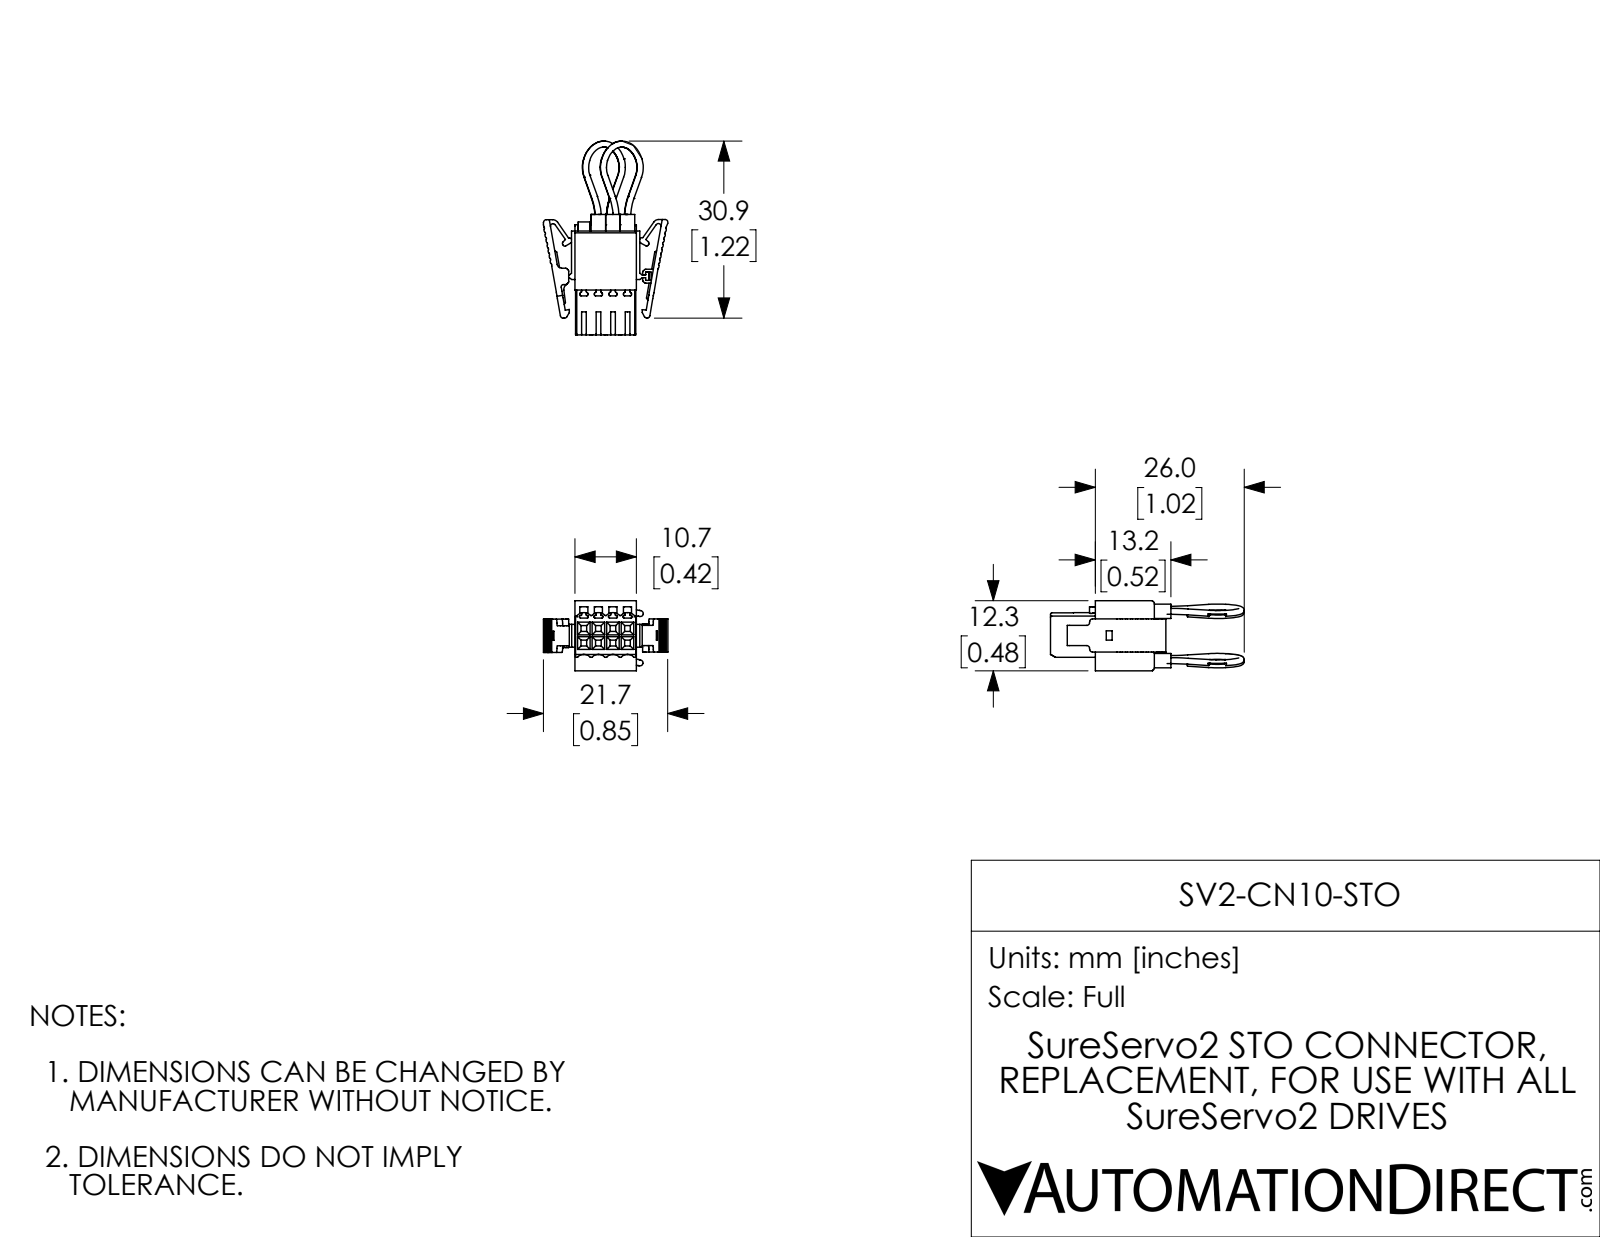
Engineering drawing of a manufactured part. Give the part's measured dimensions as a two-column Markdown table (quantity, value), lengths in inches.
| quantity | value |
| --- | --- |
| part name | SV2-CN10-STO |
| STEP written by | SolidWorks 2017 (AUTOMOTIVE_DESIGN) |
| units | inches |
| bodies | 1 solid, 703 faces (392 planar, 228 cylindrical, 83 other) |
| overall size | 1.331 × 0.855 × 0.482 |
| volume | 0.147 in³ |
| surface area | 3.9 in² |
| round bosses / shafts (diameter × count) | 0.041 × 8, 0.099 × 6 |
| partial cylindrical surfaces (radius × count) | 0.012 × 39, 0.02 × 26, 0.008 × 25, 0.004 × 8, 0.009 × 4, 0.059 × 4, 0.063 × 4, 0.006 × 3 |
| main face-to-face distances | 0.422, 0.418, 0.482, 0.035, 0.028, 0.039, 0.414, 0.157, 0.406, 0.031 |
